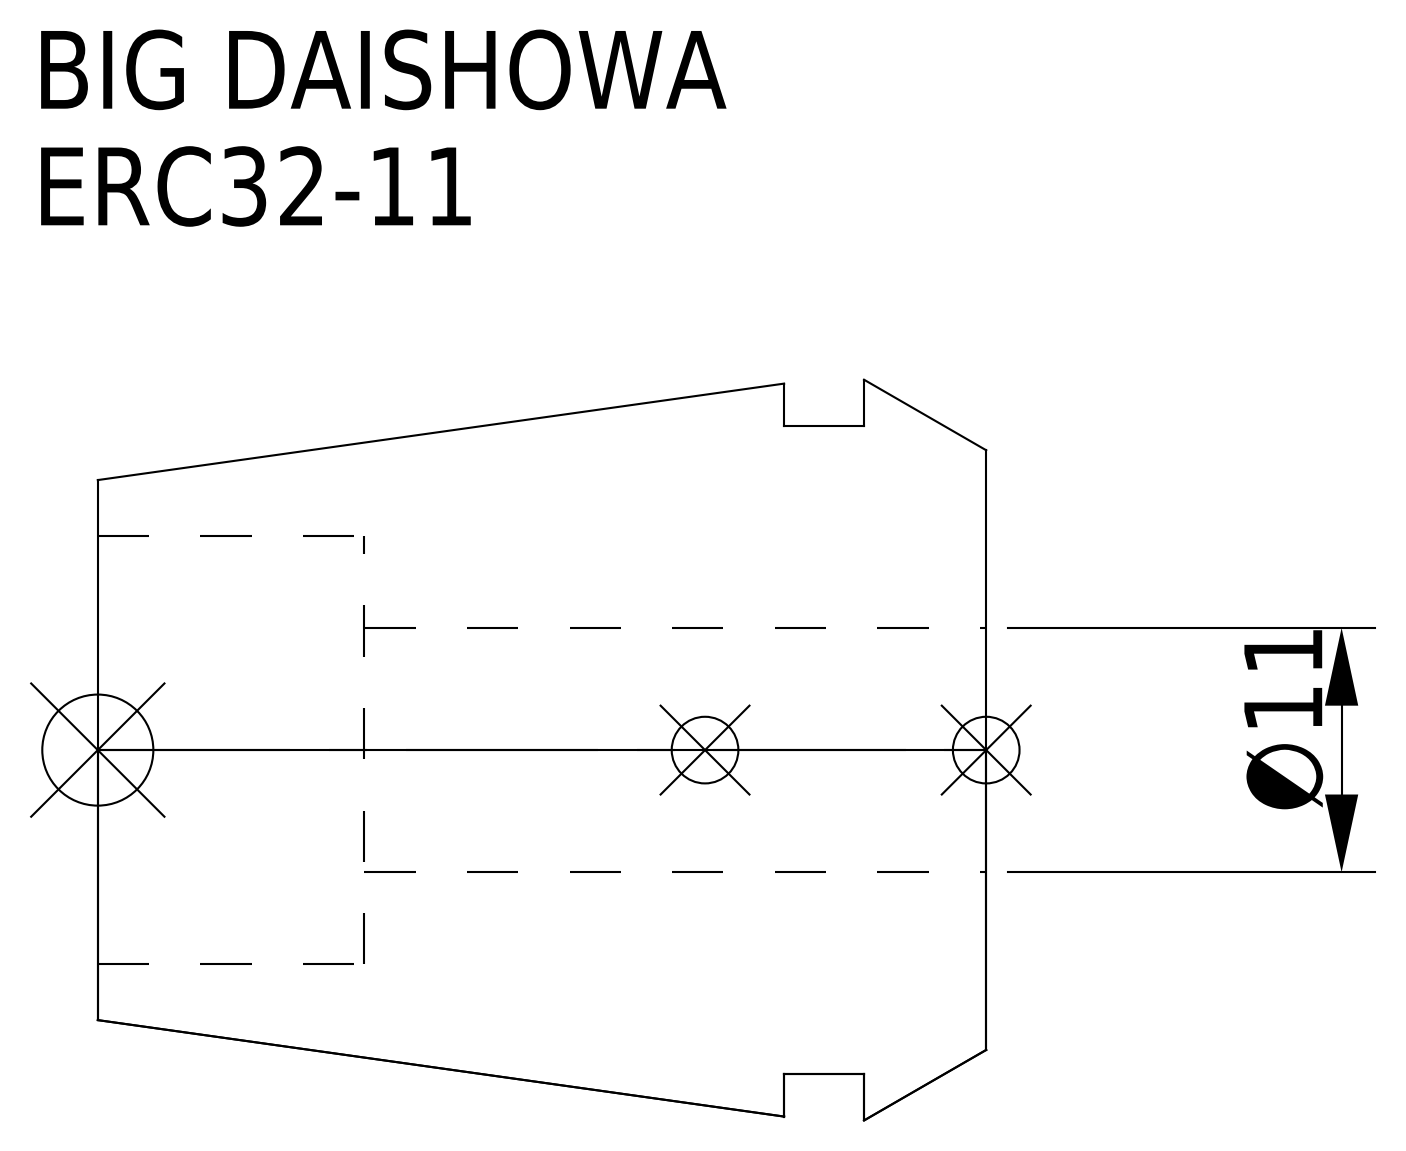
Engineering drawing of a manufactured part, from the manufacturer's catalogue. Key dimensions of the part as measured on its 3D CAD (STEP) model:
Part name (STEP PRODUCT): ERC32-11
STEP written by: CREO PARAMETRIC BY PTC INC, 2016380 (AUTOMOTIVE_DESIGN)
Units: millimetres
Bodies: 1 solid, 15 faces (5 planar, 6 cylindrical, 4 other)
Overall size (bounding box): 40 × 33.35 × 33.35
Volume: 20 271 mm³ · Surface area: 6 673 mm²
Round holes (diameter × count): ⌀11 ×1, ⌀19.3 ×1
Round bosses / shafts (diameter × count): ⌀29.2 ×1
Main face-to-face distances: 5.5, 28, 22.5, 9.1, 3.6, 18.9, 40, 34.5, 30.9, 12
